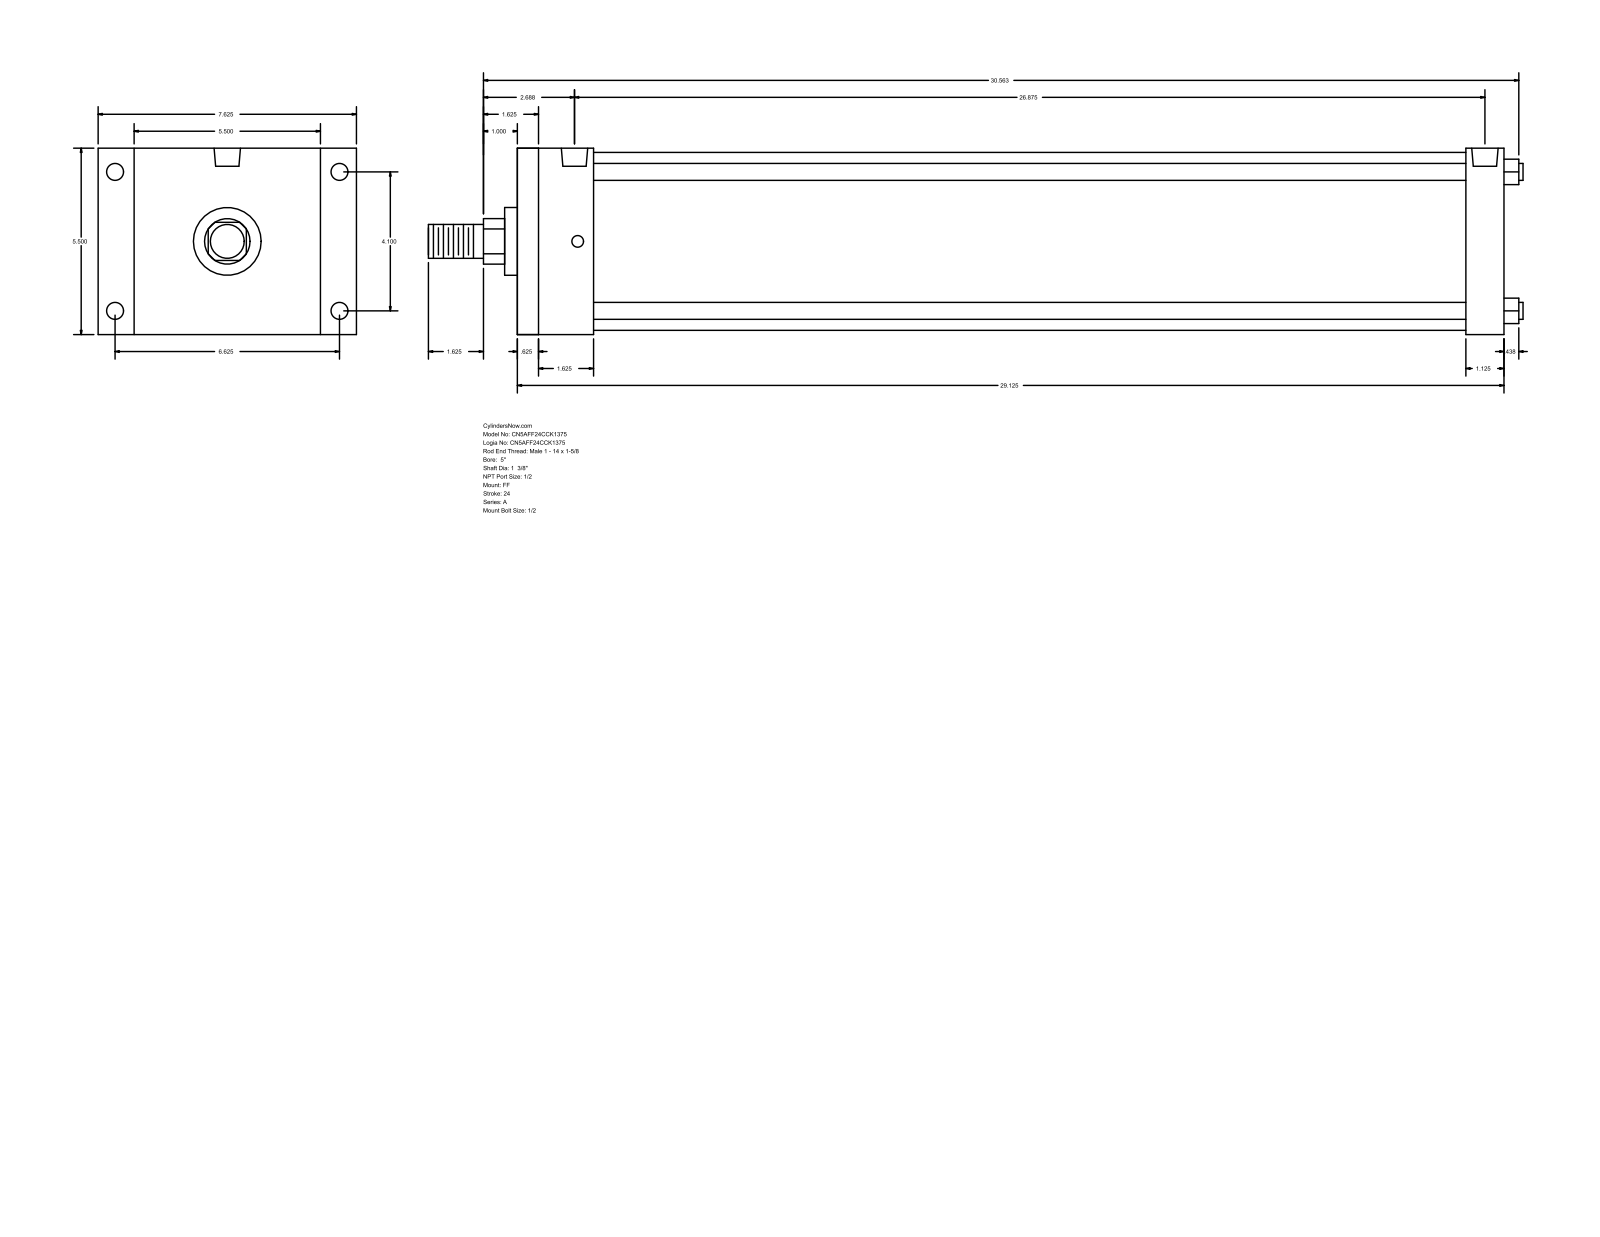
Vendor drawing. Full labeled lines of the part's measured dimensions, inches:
Part name (STEP PRODUCT): A_FF__0500_1.375
STEP written by: GSSL Pune (CONFIG_CONTROL_DESIGN)
Units: inches
Bodies: 0 solids, 92 faces (64 planar, 28 cylindrical, 0 other)
Overall size (bounding box): 32.313 × 7.625 × 5.5
Round holes (diameter × count): ⌀0.344 ×4, ⌀0.5 ×4, ⌀0.778 ×2
Round bosses / shafts (diameter × count): ⌀0.5 ×4, ⌀5.25 ×1, ⌀2 ×1, ⌀1.375 ×1, ⌀1 ×1
Partial cylindrical surfaces — rounded edges, fillets, slot ends (radius × count): R0.672 ×1
Main face-to-face distances: 5.5, 29.125, 28.5, 0.625, 2.25, 1.125, 28, 27.375, 1.625, 25.75
Hole centre spacings: 0.094, 4.1, 6.625, 7.791, 26.687, 26.781, 26.875
